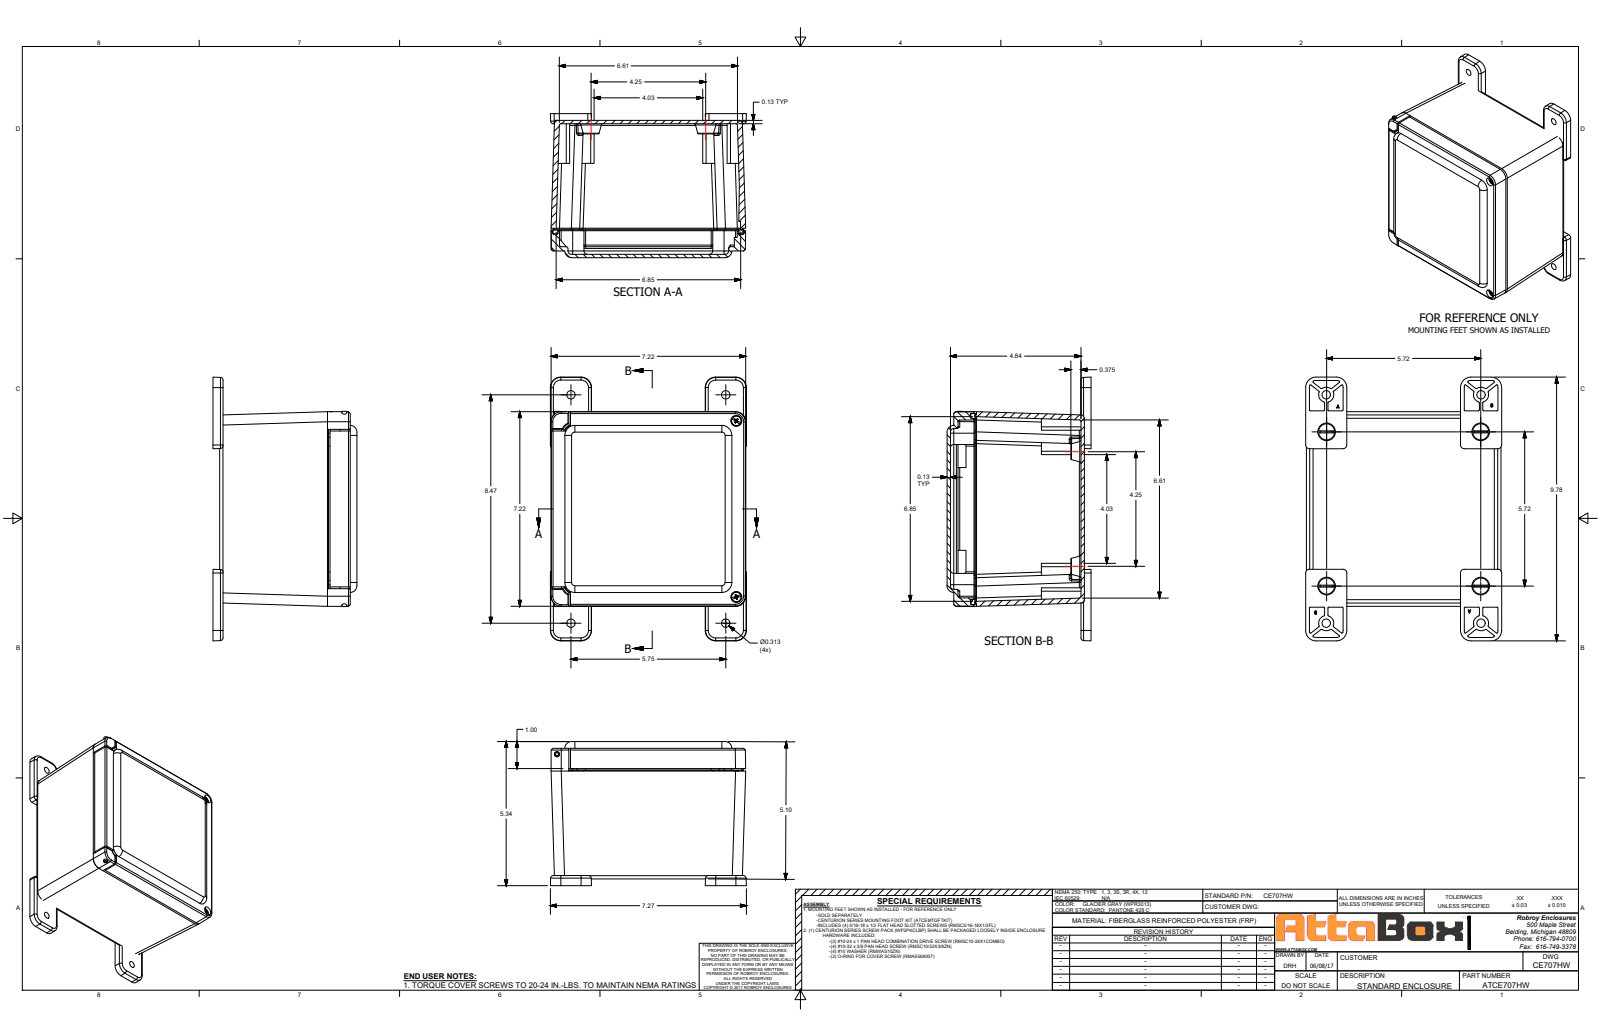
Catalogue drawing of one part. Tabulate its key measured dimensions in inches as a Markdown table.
| quantity | value |
| --- | --- |
| part name | CE707HW |
| STEP written by | SolidWorks 2018 (AUTOMOTIVE_DESIGN) |
| units | inches |
| bodies | 29 solids, 1429 faces (620 planar, 373 cylindrical, 436 other) |
| overall size | 9.783 × 7.273 × 5.344 |
| volume | 54.18 in³ |
| surface area | 601.9 in² |
| round holes (diameter × count) | 0.159 × 6, 0.281 × 6, 0.313 × 4, 0.313 × 4, 0.344 × 4, 0.531 × 4, 0.096 × 2, 0.156 × 2, 0.19 × 2, 0.219 × 2, 0.23 × 2, 0.28 × 2 |
| round bosses / shafts (diameter × count) | 0.27 × 6, 0.229 × 4, 0.375 × 2, 0.373 × 2, 0.136 × 2, 0.325 × 1, 0.325 × 1, 0.182 × 1 |
| partial cylindrical surfaces (radius × count) | 0.031 × 56, 0.031 × 50, 0.125 × 34, 0.062 × 17, 0.063 × 12, 0.1 × 12, 0.25 × 12, 0.375 × 10 |
| main face-to-face distances | 0.125, 4.969, 5.094, 0.186, 0.186, 4.844, 0.25, 0.125, 5.219, 0.75 |
| hole center spacings | 8.09, 1.039, 1.375, 2.239, 5.039, 5.04, 5.426, 5.896 |
